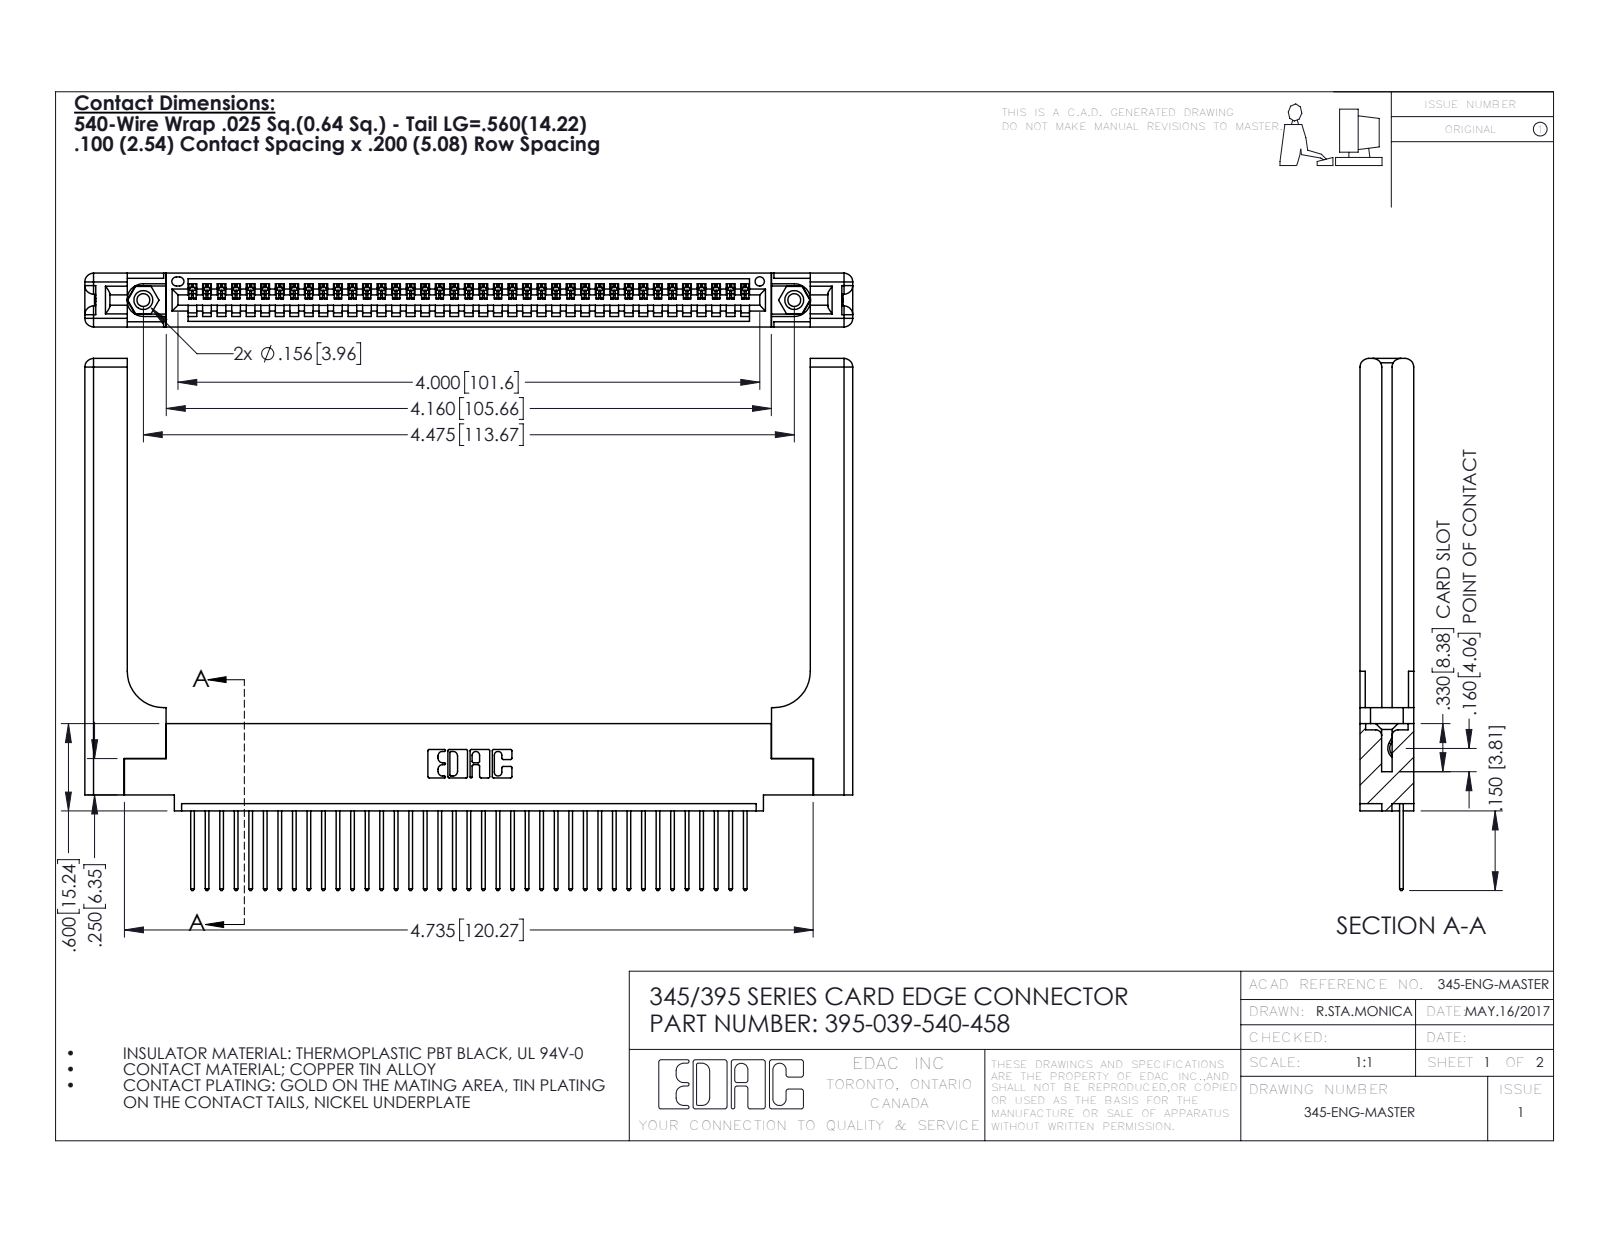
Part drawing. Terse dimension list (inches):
name: 345 Part_0.110 Offset - 0.156 Dia-TH; 345-292-001_345-293-140; 395-039-540-458; 345-220-058_345-220-058 (+1 more)
written by: SolidWorks 2016 (CONFIG_CONTROL_DESIGN)
unit: in
bodies: 44 solids, 2648 faces (1792 planar, 796 cylindrical, 60 other)
size: 5.279 × 3.657 × 0.37
volume: 1.293 in³; area: 35.02 in²
holes: 2× ⌀0.089, 2× ⌀0.125, 2× ⌀0.156, 1× ⌀0.064
bosses: 2× ⌀0.155
rounds: 78× R0.006, 78× R0.01, 22× R0.01, 16× R0.06, 6× R0.007, 6× R0.031, 3× R0.026, 2× R0.03
face distances: 0.072, 0.37, 0.298, 0.098, 0.272, 0.025, 0.2, 0.148, 0.15, 0.225
hole spacings: 0.27, 4.239, 4.475
